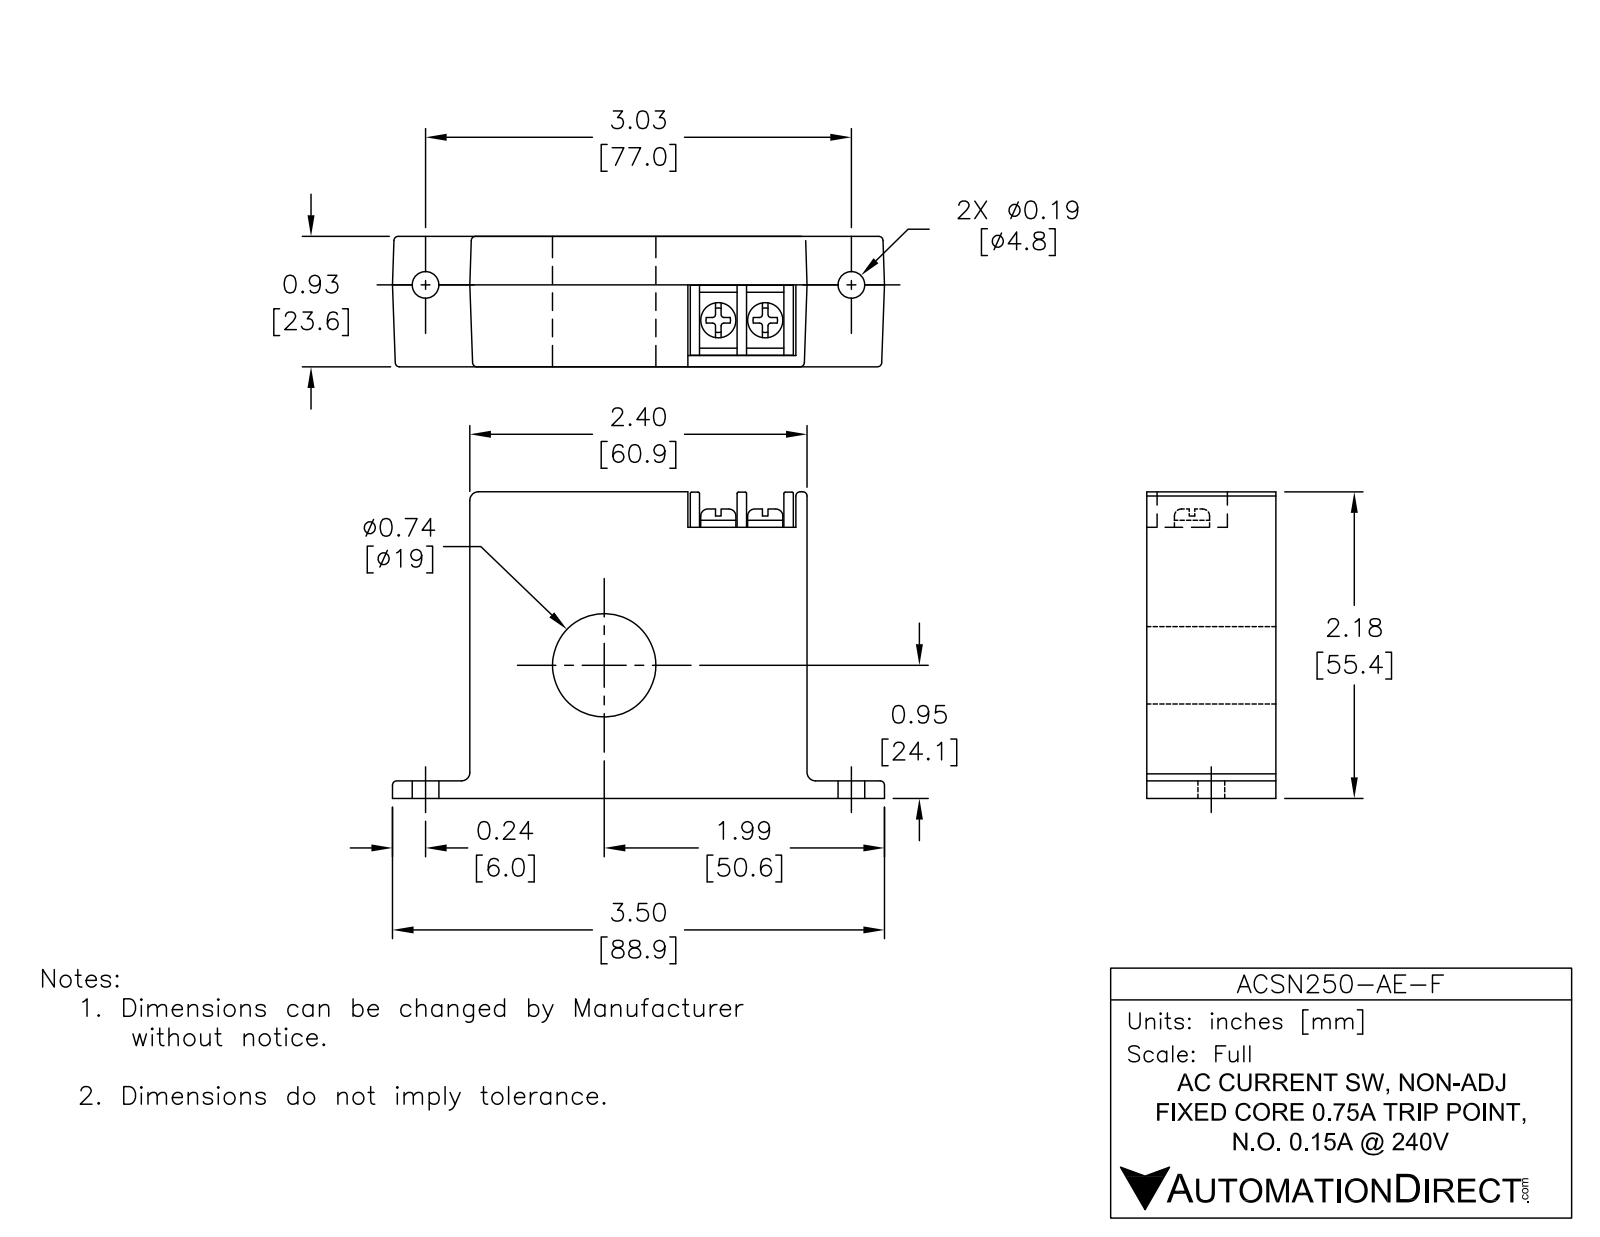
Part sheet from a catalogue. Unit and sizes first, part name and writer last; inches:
Units: inches
Overall size (bounding box): 3.53 × 2.214 × 0.938
Round holes (diameter × count): ⌀0.195 ×1, ⌀0.195 ×1, ⌀0.747 ×1
Round bosses / shafts (diameter × count): ⌀0.221 ×2, ⌀0.15 ×2
Partial cylindrical surfaces — rounded edges, fillets, slot ends (radius × count): R0.016 ×30, R0.03 ×2
Main face-to-face distances: 0.938, 2.42, 2.185, 0.155, 2.03, 0.319, 1.927, 1.772, 0.258, 0.056
Hole centre spacings: 3.025
Volume: 4.563 in³ · Surface area: 24.06 in²
Bodies: 1 solid, 176 faces (94 planar, 50 cylindrical, 32 other)
Part name (STEP PRODUCT): ACSN250-AE-F
STEP written by: SolidWorks 2014 (AUTOMOTIVE_DESIGN)
